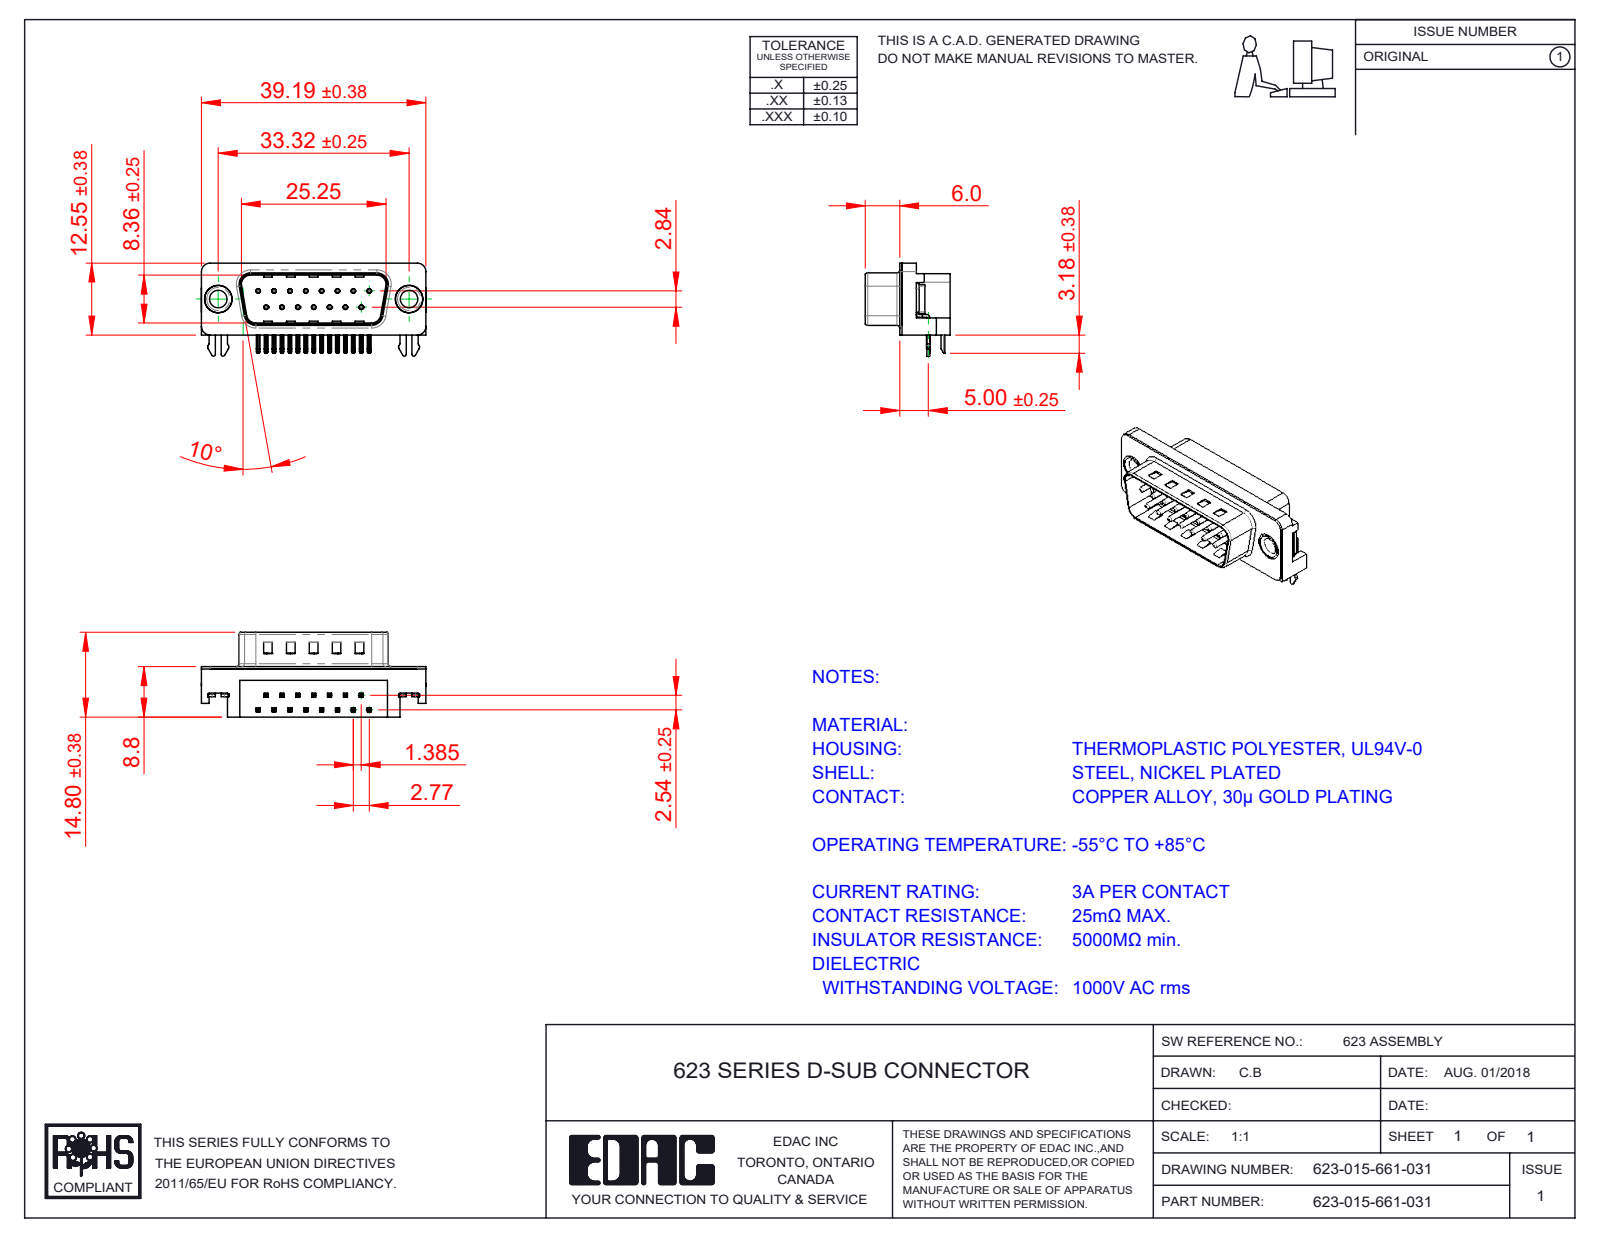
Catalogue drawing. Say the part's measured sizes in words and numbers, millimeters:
The part is named "623 Shell_15 Socket; 623-015-661-031; 623 Contact Top; 623 2 Prong Board Lock (+3 more)". Its 3-D file was written by "SolidWorks 2016 (CONFIG_CONTROL_DESIGN)". It is 21 solids with 1459 faces: 921 planar, 421 cylindrical and 117 other. Overall it measures 39.22 by 16.25 by 14.8 millimeters. Its volume is 3 315 cubic millimeters and its surface area 4 923 square millimeters. Round holes: 15 of diameter 0.35, 15 of diameter 0.8, 2 of diameter 3.05, 2 of diameter 4, 2 of diameter 4.8, 2 of diameter 5. Round bosses or shafts: 15 of diameter 0.75, 2 of diameter 4.9, 2 of diameter 4.75, 2 of diameter 3.85. Partial cylindrical surfaces (rounded edges, fillets, slot ends): 68 of radius 0.25, 30 of radius 0.12, 14 of radius 0.5, 8 of radius 1, 6 of radius 1.5, 4 of radius 0.32, 4 of radius 0.9, 4 of radius 1.6. The main face-to-face distances are 0.4, 8.4, 2.1, 1.7, 8.8, 10.46, 10.86, 8.76, 5.9, 2.9. The hole center spacings are 3.16, 2.77, 5.54, 8.31, 11.08, 5.03, 5.04, 7.48.
